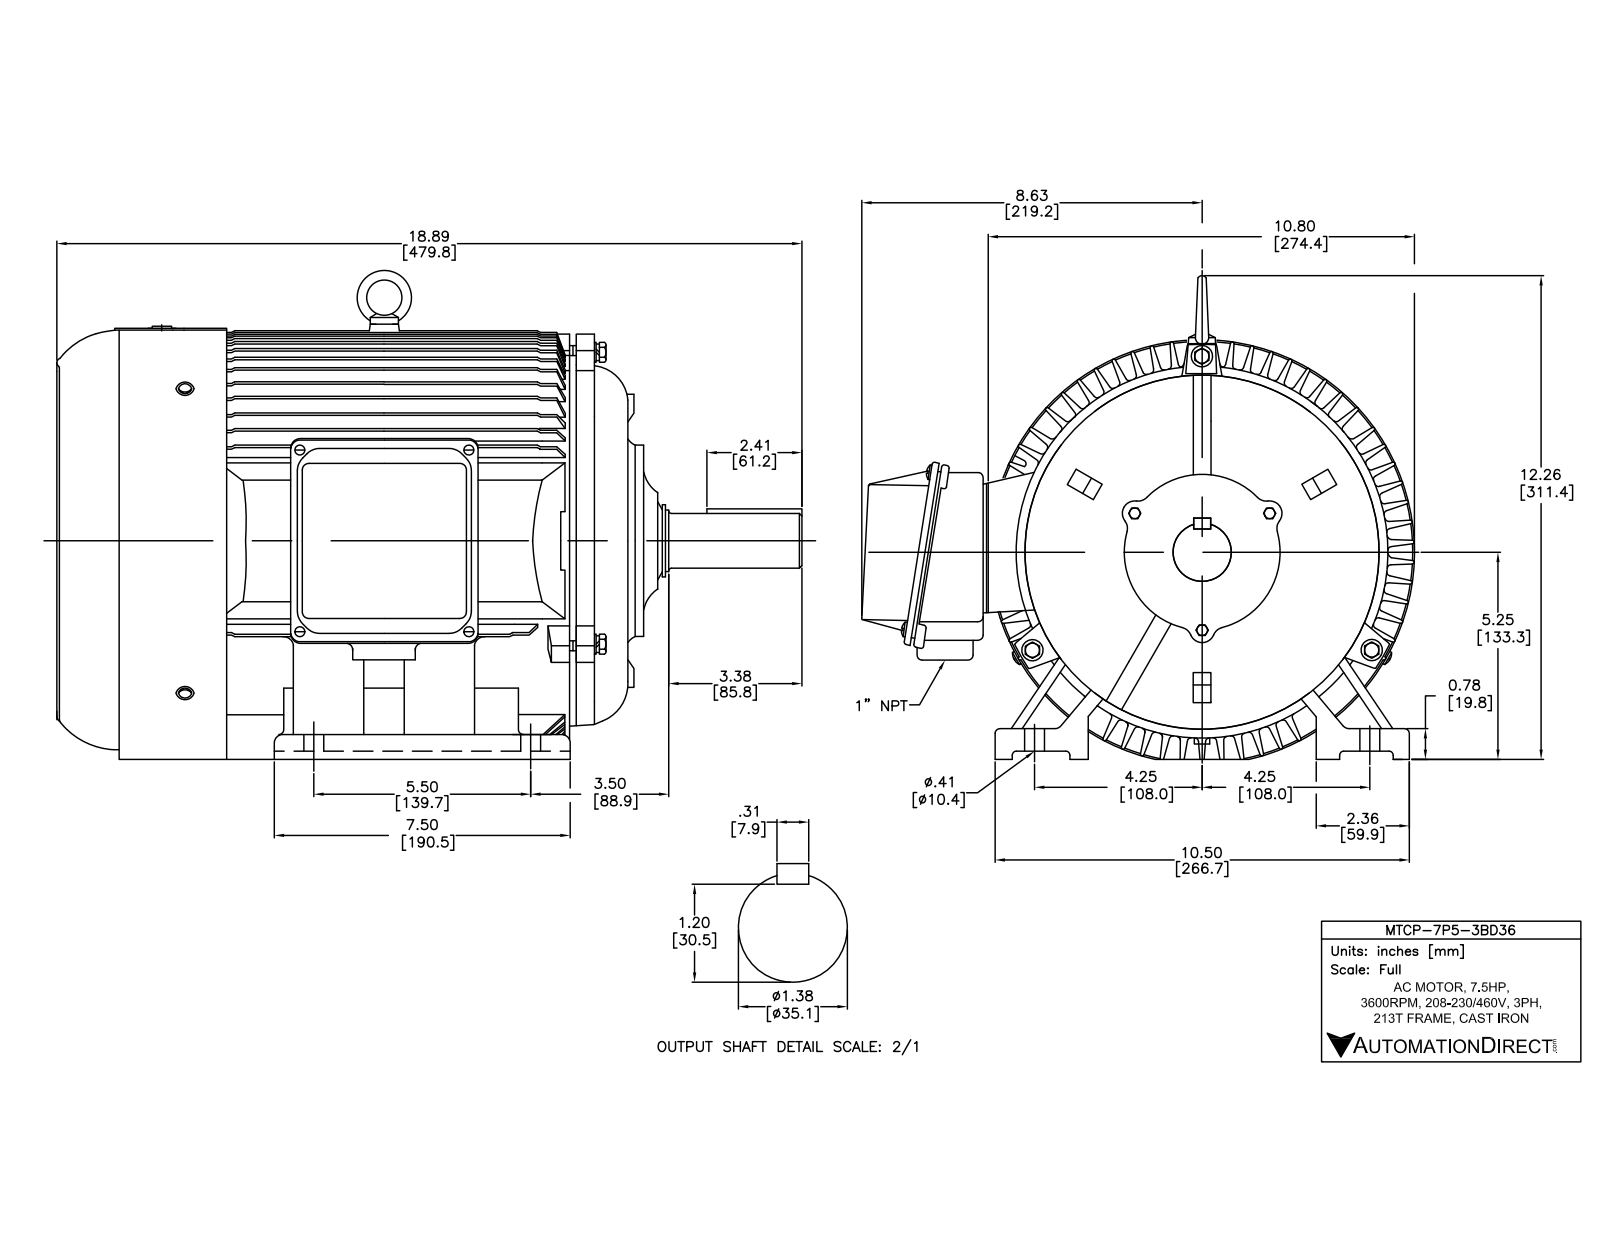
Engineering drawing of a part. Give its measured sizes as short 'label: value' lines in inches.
name: N213T 3D ADC
written by: SolidWorks 2017 (AUTOMOTIVE_DESIGN)
unit: in
bodies: 19 solids, 1763 faces (1017 planar, 478 cylindrical, 268 other)
size: 17.835 × 13.362 × 11.986
volume: 230.2 in³; area: 1 882 in²
holes: 8× ⌀0.228, 6× ⌀0.197, 4× ⌀0.165, 4× ⌀0.236, 4× ⌀0.276, 4× ⌀0.433, 3× ⌀0.315, 3× ⌀0.362, 3× ⌀0.394, 1× ⌀0.335, 1× ⌀0.453, 1× ⌀1
bosses: 7× ⌀0.197, 3× ⌀0.283, 1× ⌀10.173, 1× ⌀10.079, 1× ⌀8.898, 1× ⌀5.118, 1× ⌀4.173, 1× ⌀3.317
rounds: 93× R0.118, 32× R0.051, 25× R0.276, 12× R0.039, 9× R0.059, 6× R0.091, 6× R0.433, 4× R0.079
face distances: 0.157, 14.207, 0.709, 0.047, 14.254, 0.177, 0.531, 0.236, 13.97, 14.018
hole spacings: 3.937, 2.677, 4.331, 5.853, 2.678, 3.786, 4.331, 5.853
